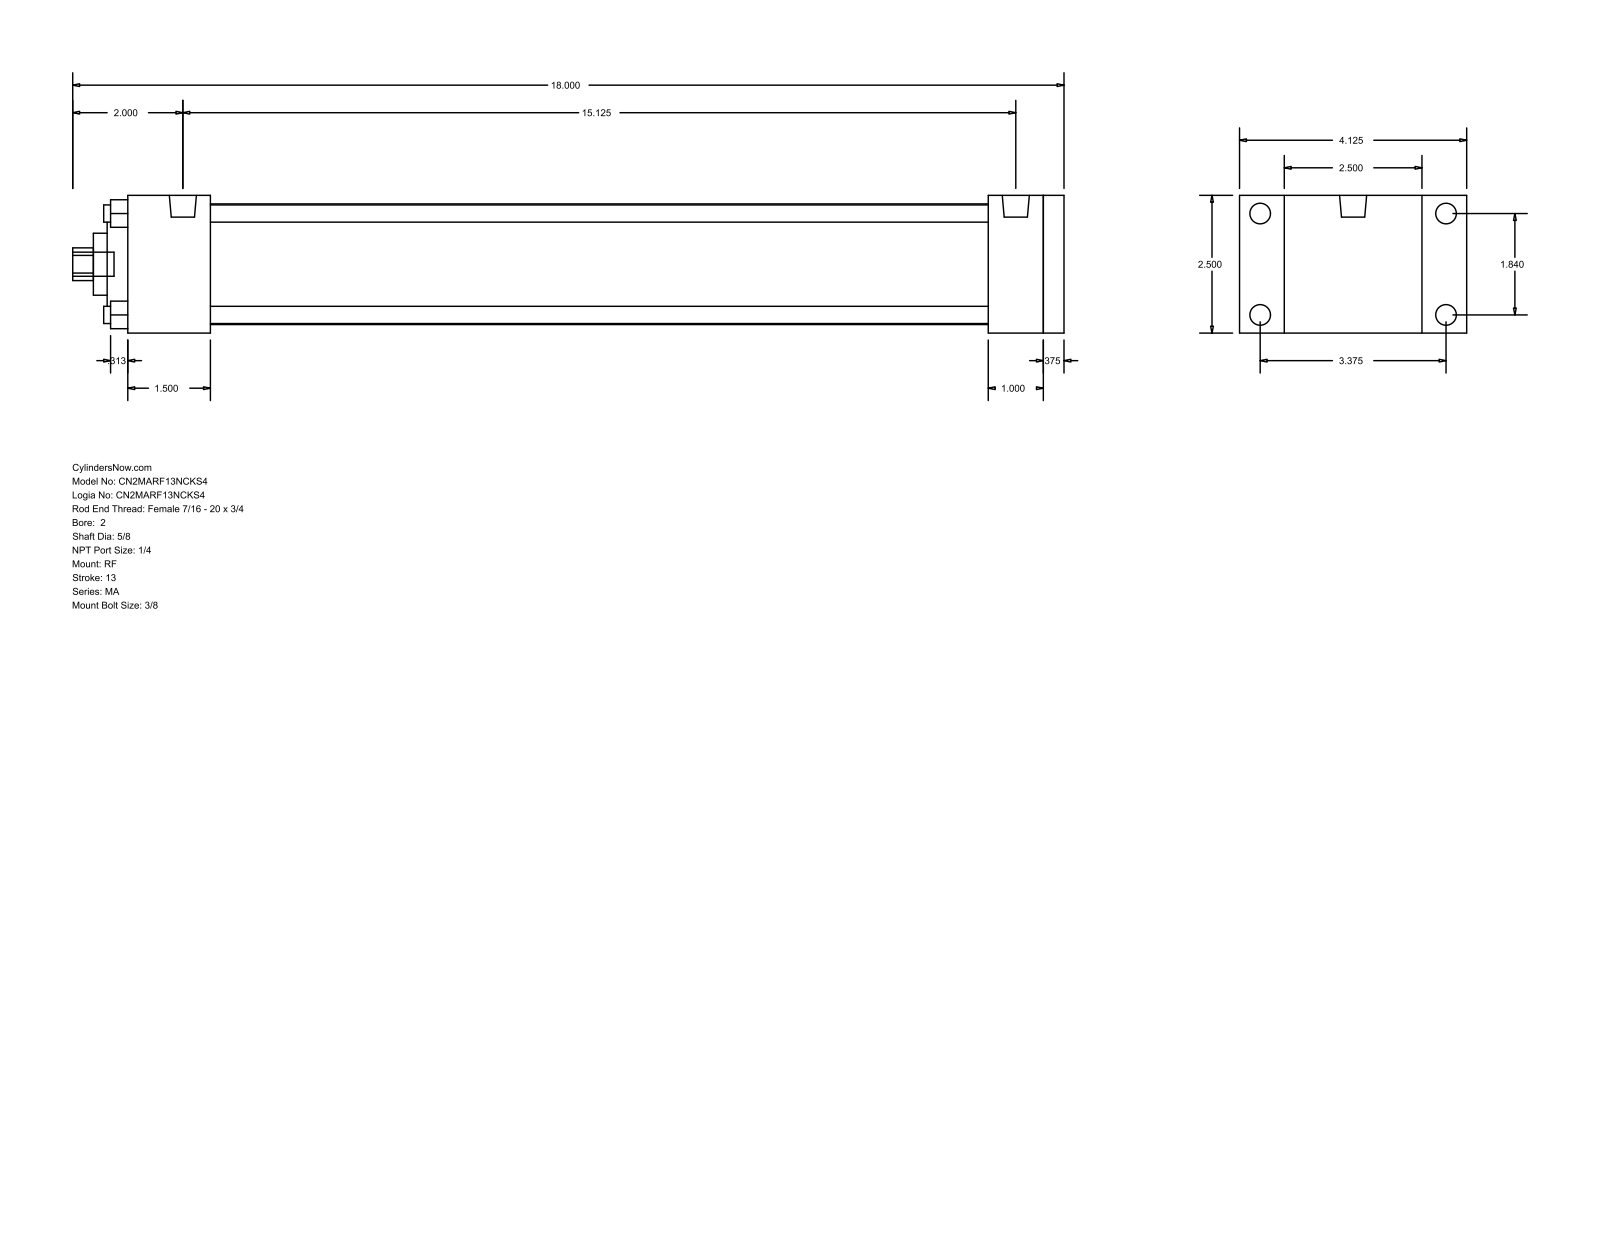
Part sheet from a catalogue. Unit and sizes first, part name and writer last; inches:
Units: inches
Overall size (bounding box): 18 × 4.125 × 2.5
Round holes (diameter × count): ⌀0.313 ×4, ⌀0.625 ×1, ⌀1.125 ×1, ⌀2 ×1, ⌀2.19 ×1
Round bosses / shafts (diameter × count): ⌀0.375 ×4, ⌀0.313 ×4, ⌀0.492 ×2, ⌀0.437 ×1
Partial cylindrical surfaces — rounded edges, fillets, slot ends (radius × count): R0.297 ×1
Main face-to-face distances: 2.5, 0.375, 17, 1.5, 16.625, 15.125, 15.5, 15.625, 14.125, 1
Hole centre spacings: 1.301, 1.84, 2.602
Bodies: 0 solids, 94 faces (65 planar, 29 cylindrical, 0 other)
Part name (STEP PRODUCT): MA_RF__0200_0.625
STEP written by: GSSL Pune (CONFIG_CONTROL_DESIGN)
